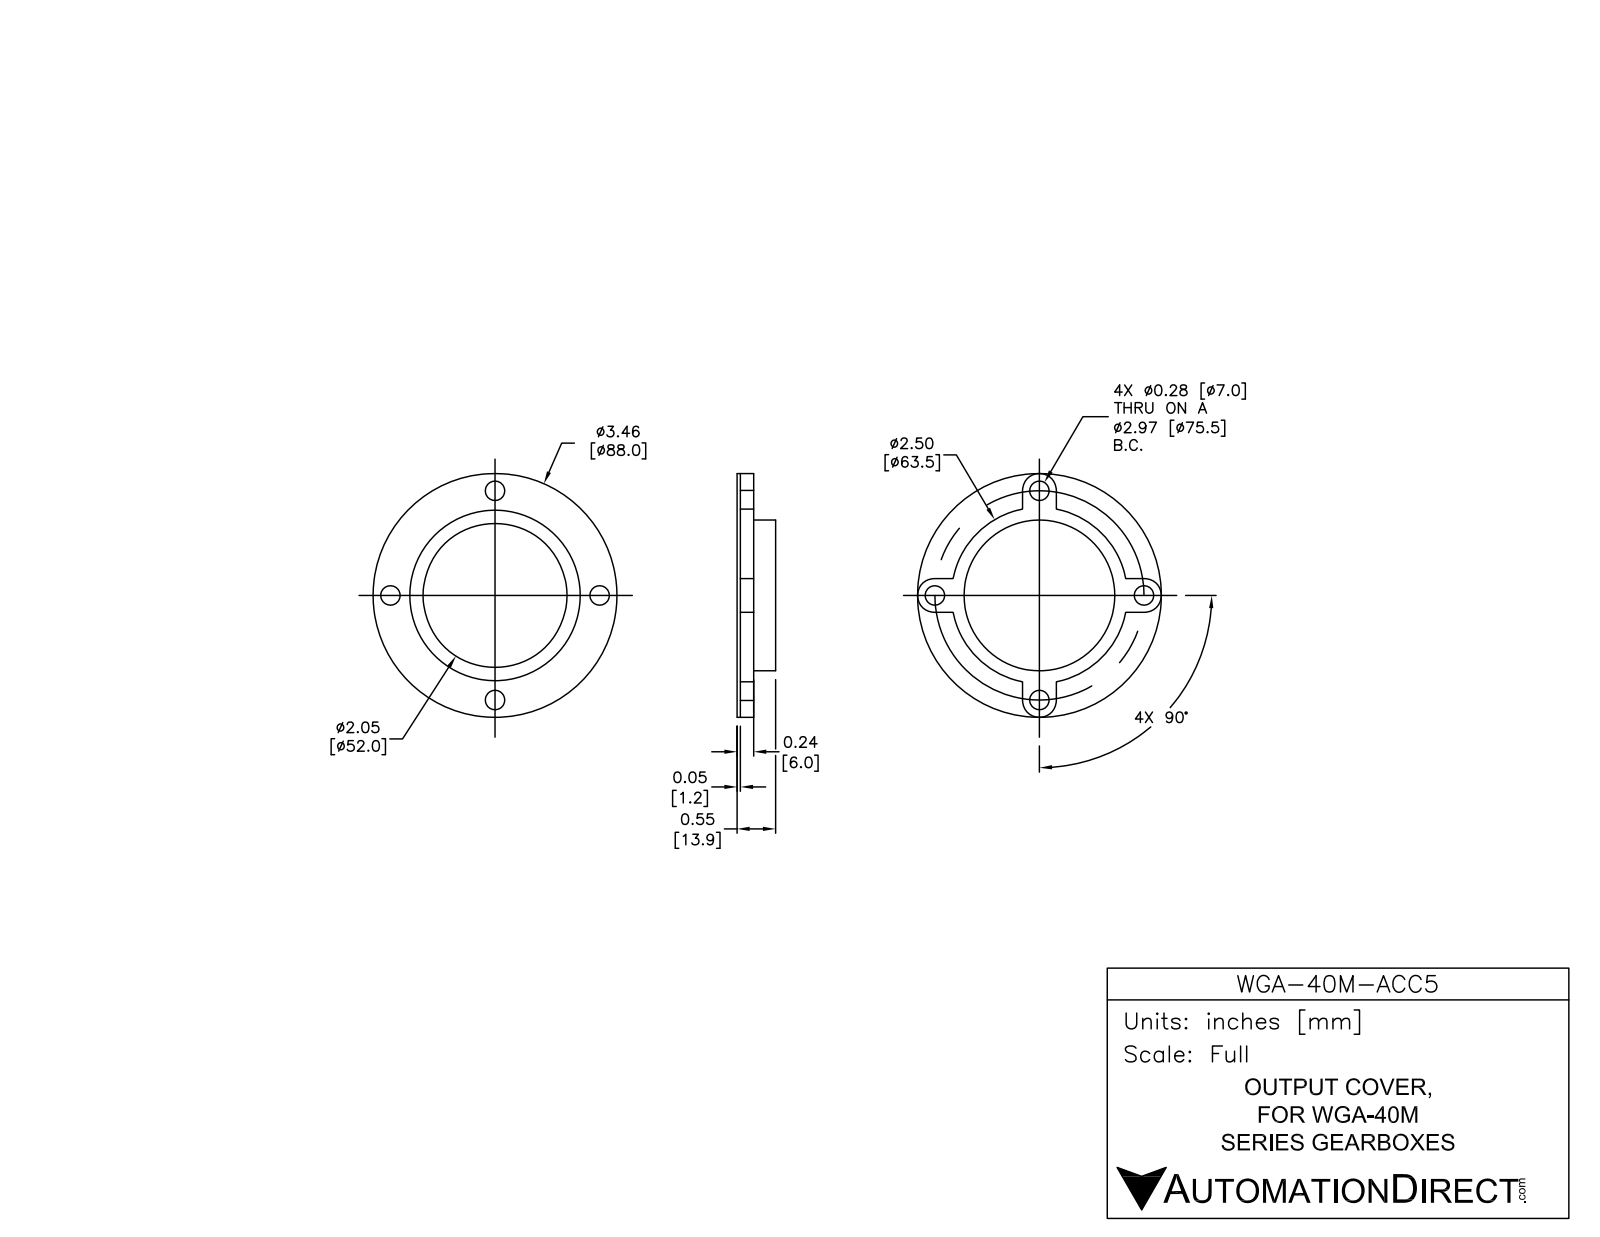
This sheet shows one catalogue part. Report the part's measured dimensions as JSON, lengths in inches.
{"part_name": "WGA-40M-ACC5", "step_written_by": "SolidWorks 2014 (AUTOMOTIVE_DESIGN)", "units": "inches", "bodies": {"solids": 1, "faces": 42, "planar": 17, "cylindrical": 25, "other": 0}, "overall_size": [3.465, 3.465, 0.547], "volume_in3": 0.702, "surface_area_in2": 27.33, "round_holes": [[0.276, 4], [2.047, 1], [2.421, 1]], "round_bosses_or_shafts": [[3.465, 1], [2.142, 1]], "partial_cylinders_radius": [[0.24, 4], [1.25, 1]], "face_to_face_distances": [0.047, 0.5, 0.547, 0.453, 0.311, 0.189, 0.264, 0.236, 0.358, 0.142], "hole_center_spacings": [1.486, 2.102, 2.972]}
